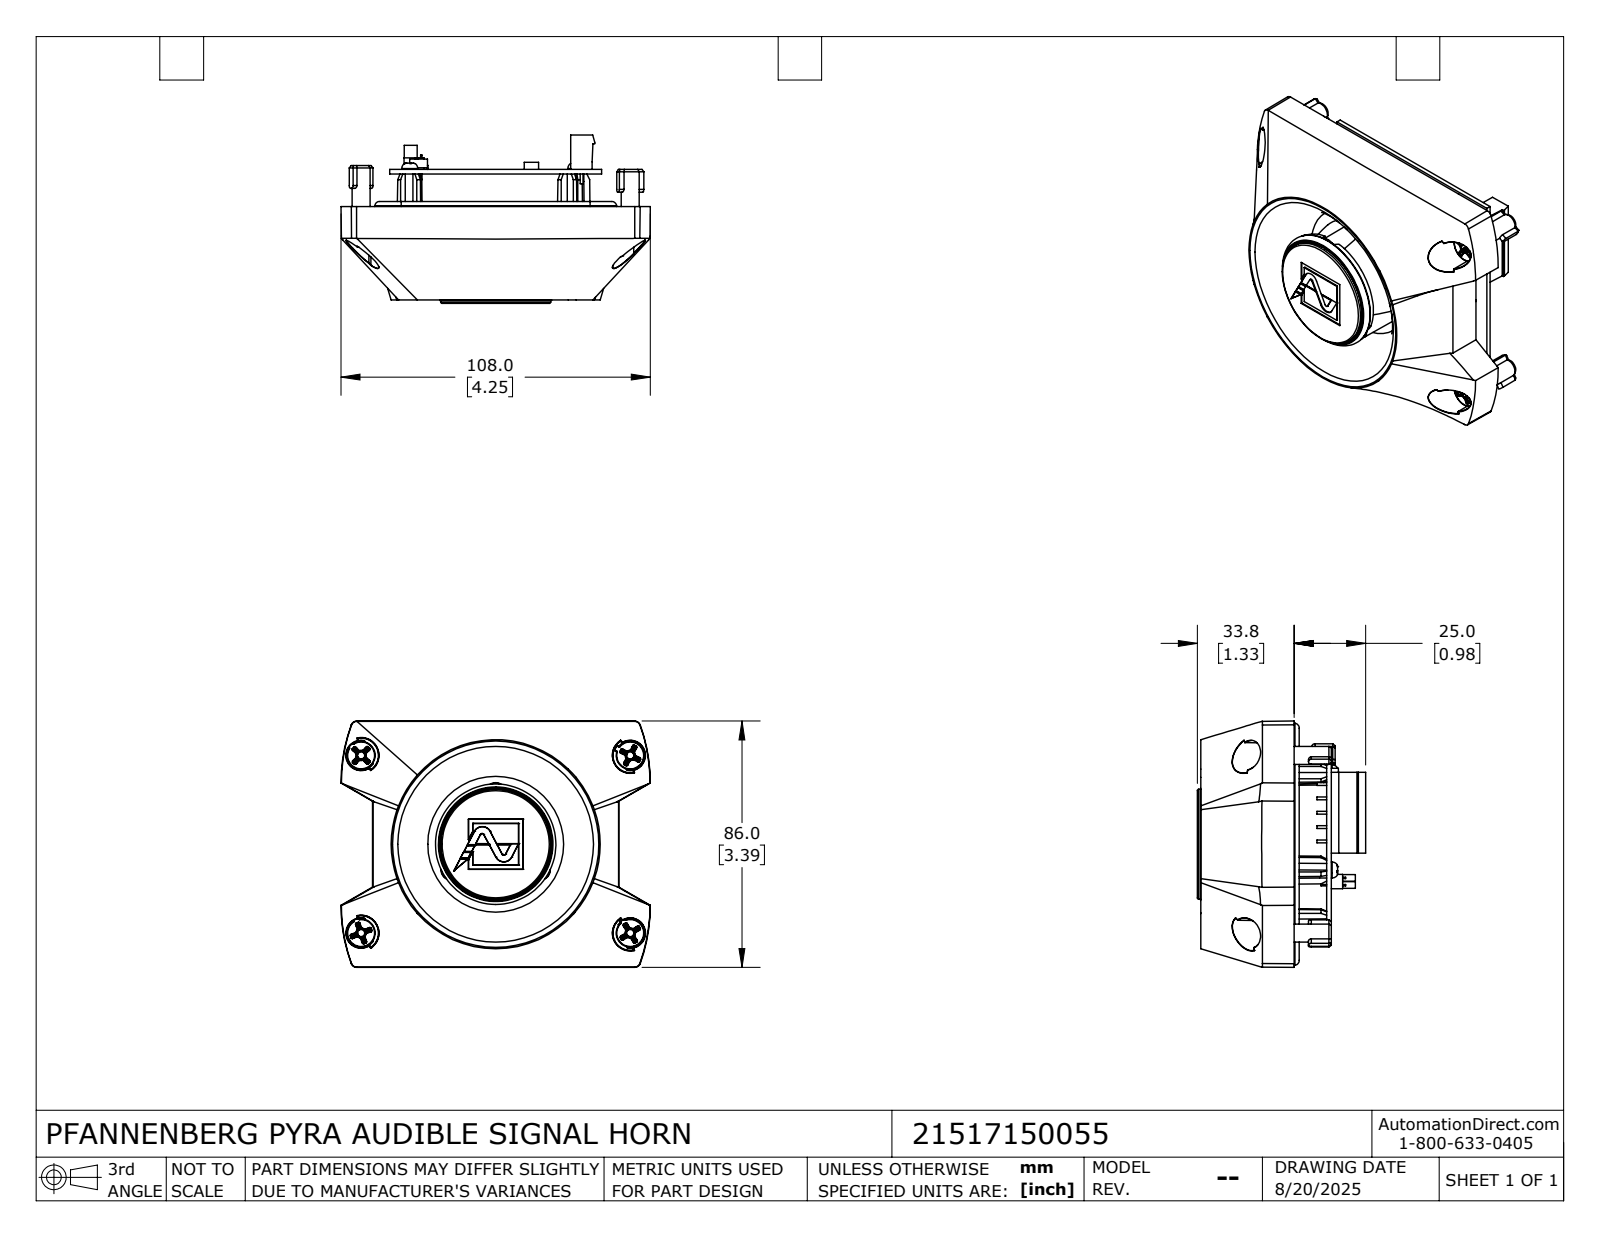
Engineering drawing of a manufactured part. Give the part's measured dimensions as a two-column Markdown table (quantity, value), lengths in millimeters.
| quantity | value |
| --- | --- |
| part name | 21517150055 |
| STEP written by | SolidWorks 2024 (CONFIG_CONTROL_DESIGN) |
| units | millimeters |
| bodies | 9 solids, 1957 faces (948 planar, 243 cylindrical, 766 other) |
| overall size | 108 × 86 × 58.77 |
| volume | 215 147 mm³ |
| surface area | 52 749 mm² |
| round holes (diameter × count) | 1 × 2, 1.5 × 2, 3 × 2, 2.5 × 1 |
| round bosses / shafts (diameter × count) | 2.8 × 5, 9.8 × 4, 6.3 × 4, 5.6 × 2, 2.9 × 2, 42.05 × 1, 2.3 × 1 |
| partial cylindrical surfaces (radius × count) | 0.2 × 94, 3 × 5, 1 × 4, 1.74 × 4, 5.1 × 4, 0.1 × 2, 5.9 × 2, 10.02 × 2 |
| main face-to-face distances | 12.97, 1.6, 11.37, 33.8, 46.77, 45.17, 2, 86, 19.5, 2.8 |
| hole center spacings | 5, 12.54, 17.2, 20.8, 22.15, 25.74, 33.09, 34.13 |
